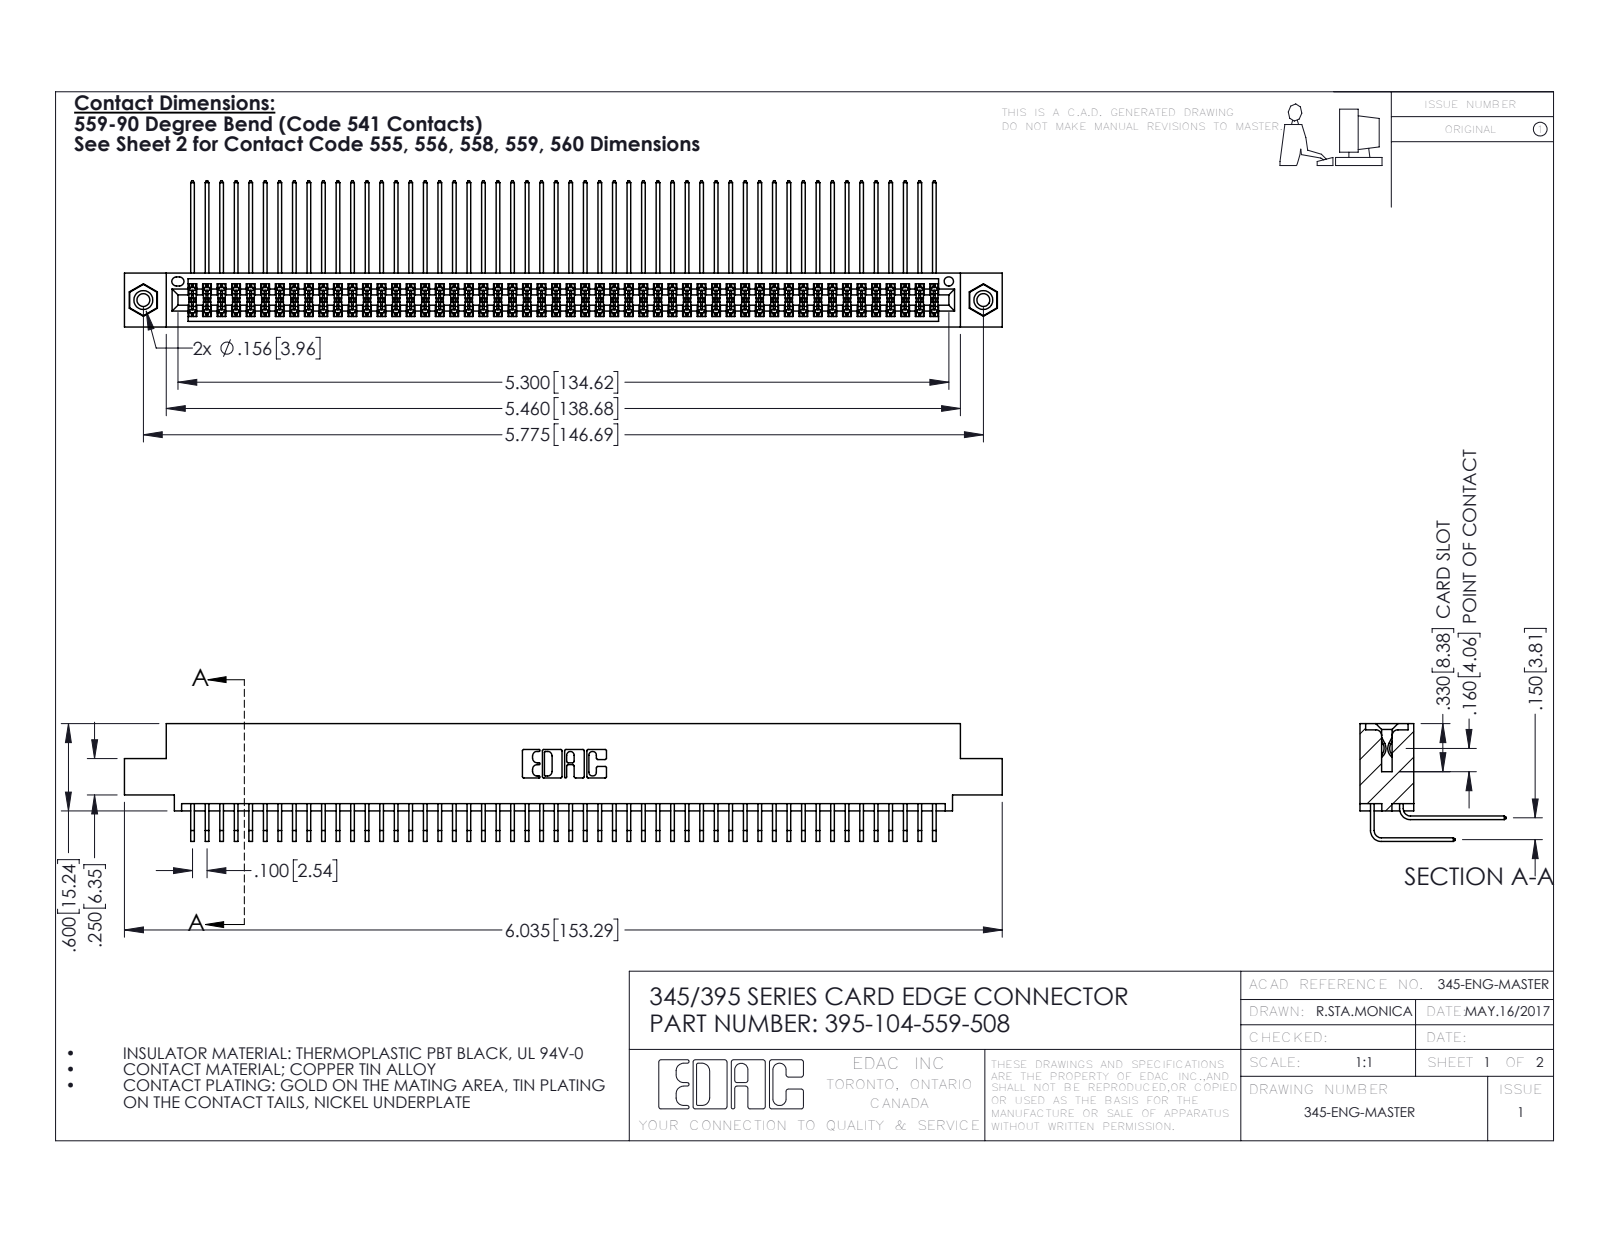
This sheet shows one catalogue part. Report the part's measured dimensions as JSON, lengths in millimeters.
{"part_name": "345-292-001_559 Tail - 2; 345-292-001_558 559 Tail - 1; 345-250-001_345-250-003-102; 395-104-559-508 (+1 more)", "step_written_by": "SolidWorks 2016 (CONFIG_CONTROL_DESIGN)", "units": "millimeters", "bodies": {"solids": 107, "faces": 5598, "planar": 3756, "cylindrical": 1826, "other": 16}, "overall_size": [153.3, 25.5, 20.5], "volume_mm3": 15500, "surface_area_mm2": 26040, "round_holes": [[2.3, 2], [3.2, 2], [4, 2], [1.6, 1]], "round_bosses_or_shafts": [[3.9, 2]], "partial_cylinders_radius": [[0.2, 156], [0.3, 22], [0.2, 6], [0.8, 6], [0.7, 3], [0.4, 2], [0.5, 2], [0.6, 2]], "face_to_face_distances": [1.8, 7.6, 5.1, 9.4, 2.5, 6.9, 0.6, 5.7, 4.4, 3.8], "hole_center_spacings": [6.9, 140.7, 146.7]}
